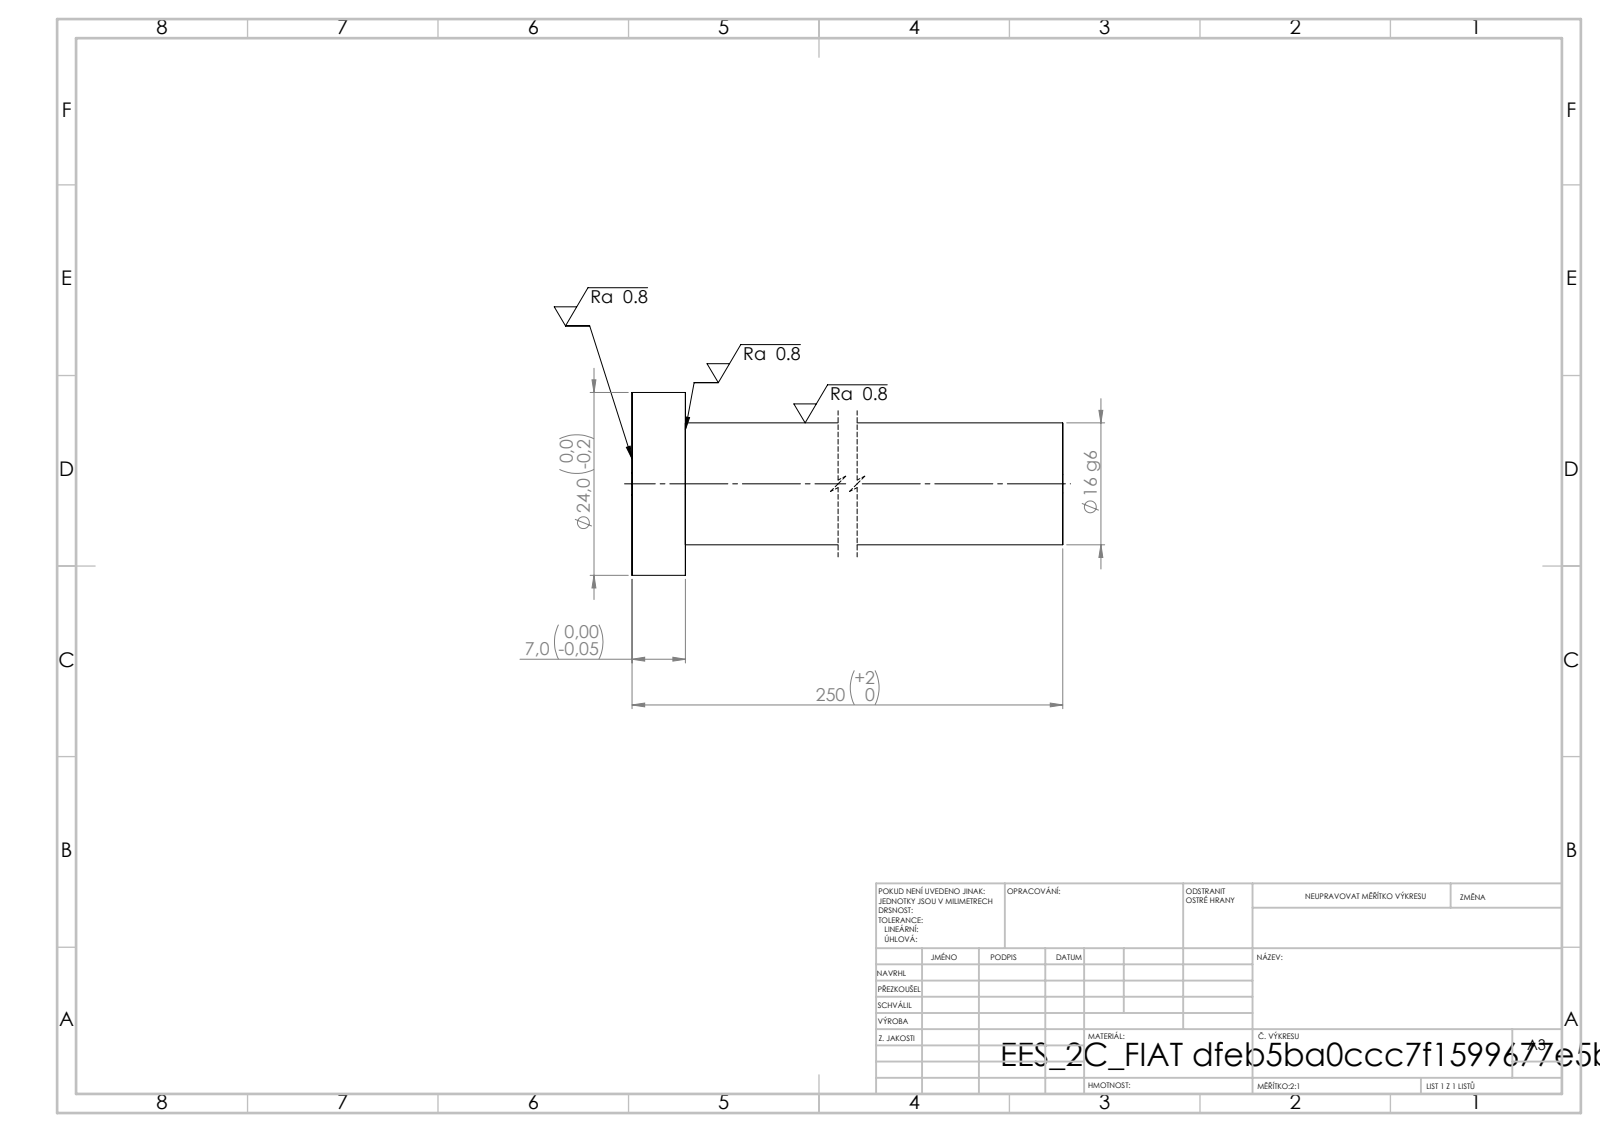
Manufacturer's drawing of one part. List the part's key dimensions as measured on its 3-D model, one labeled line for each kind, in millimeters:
STEP written by: SolidWorks 2019 (CONFIG_CONTROL_DESIGN)
Units: millimetres
Bodies: 1 solid, 7 faces (3 planar, 4 cylindrical, 0 other)
Overall size (bounding box): 250 × 24 × 24
Volume: 52 025 mm³ · Surface area: 13 647 mm²
Round bosses / shafts (diameter × count): ⌀24 ×1, ⌀16 ×1
Main face-to-face distances: 7, 250, 243
